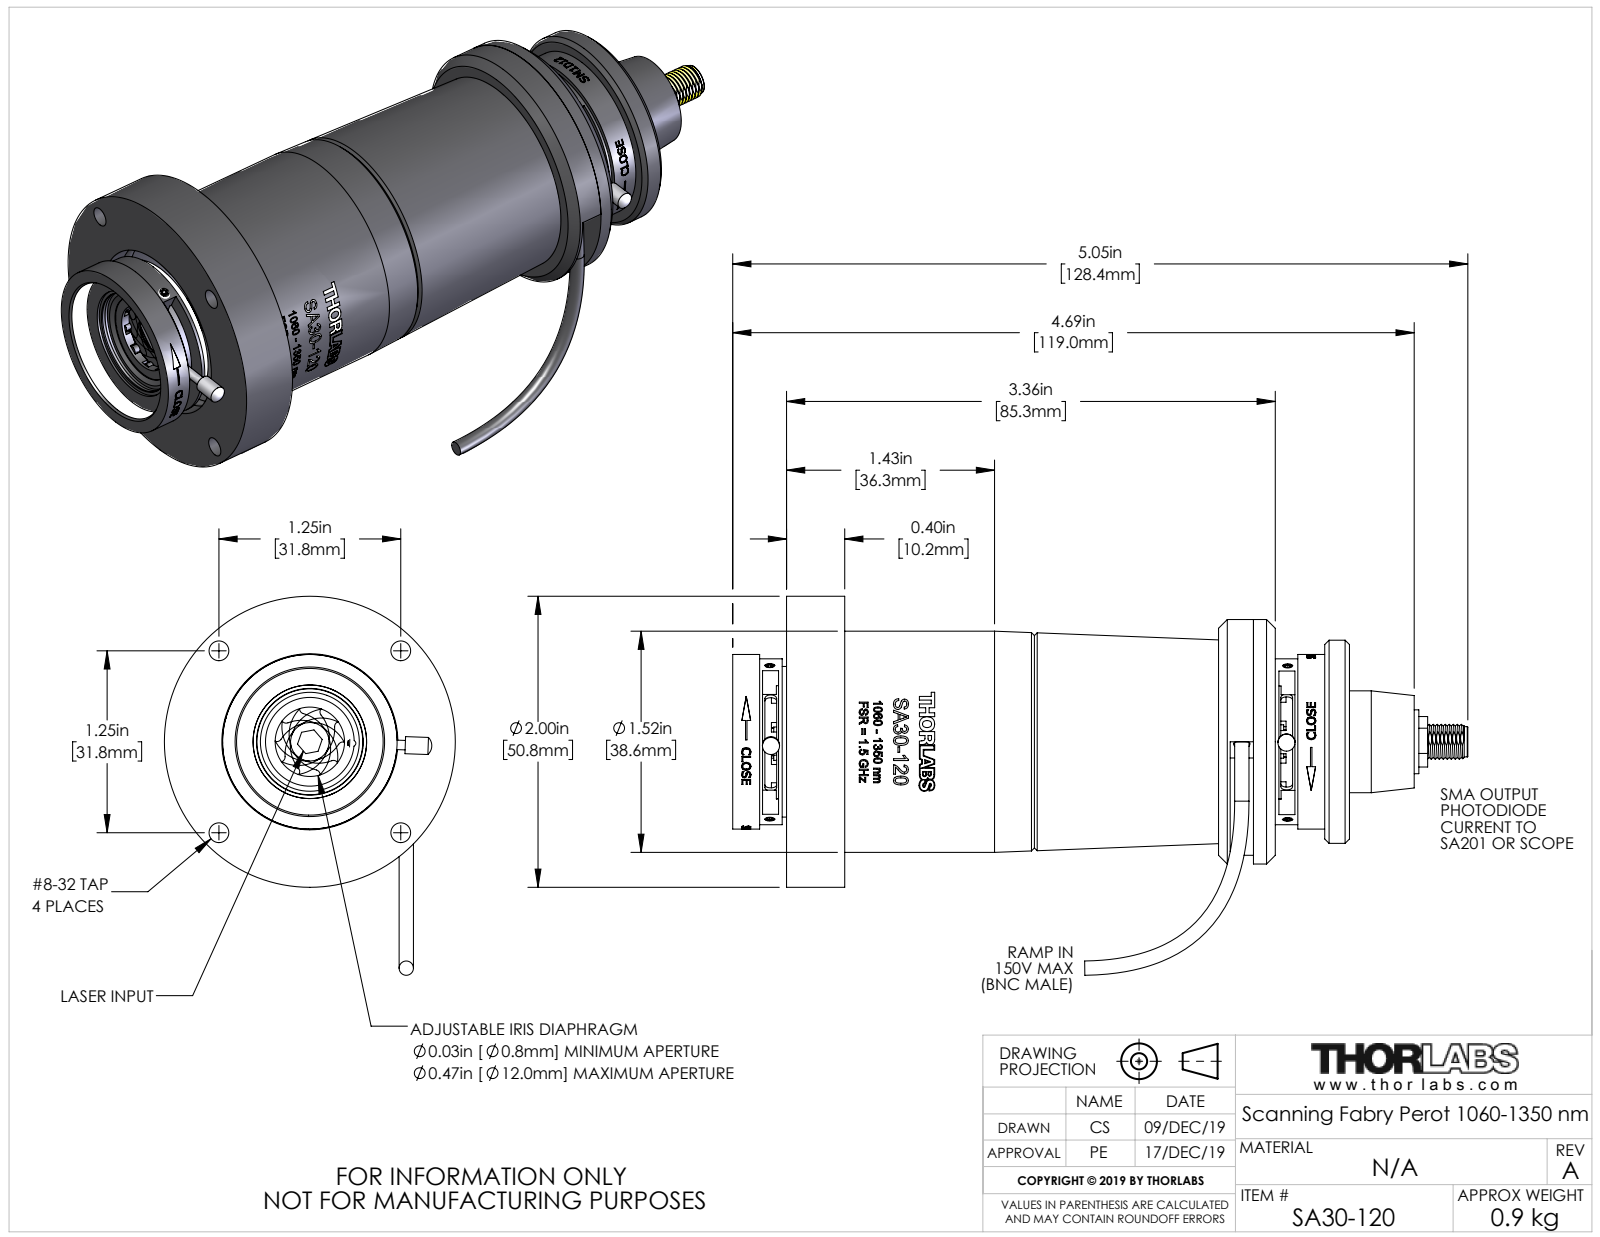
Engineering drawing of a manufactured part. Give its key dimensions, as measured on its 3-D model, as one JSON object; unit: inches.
{"part_name": "STN052140-E0W", "step_written_by": "SolidWorks 2018 (AUTOMOTIVE_DESIGN)", "units": "inches", "bodies": {"solids": 42, "faces": 1579, "planar": 619, "cylindrical": 534, "other": 426}, "overall_size": [5.054, 2.605, 2], "volume_in3": 3.331, "surface_area_in2": 71.3, "round_holes": [[0.066, 20], [0.136, 4], [0.043, 2], [0.063, 2], [0.039, 1], [0.113, 1], [0.181, 1], [0.25, 1], [0.325, 1], [0.385, 1], [0.4, 1], [0.474, 1]], "round_bosses_or_shafts": [[0.06, 20], [0.065, 15], [0.065, 7], [0.086, 4], [0.117, 2], [0.064, 2], [2, 1], [1.68, 1]], "partial_cylinders_radius": [[0.033, 20], [0.033, 20], [0.063, 20], [0.251, 20], [0.378, 20], [0.024, 2], [0.13, 2], [1, 2]], "face_to_face_distances": [3.21, 0.15, 3.418, 0.51, 3.375, 0.045, 3.373, 0.043, 0.4, 2.81], "hole_center_spacings": [0.343, 0.472, 0.292, 0.556, 0.584, 0.172, 0.18, 0.181]}
